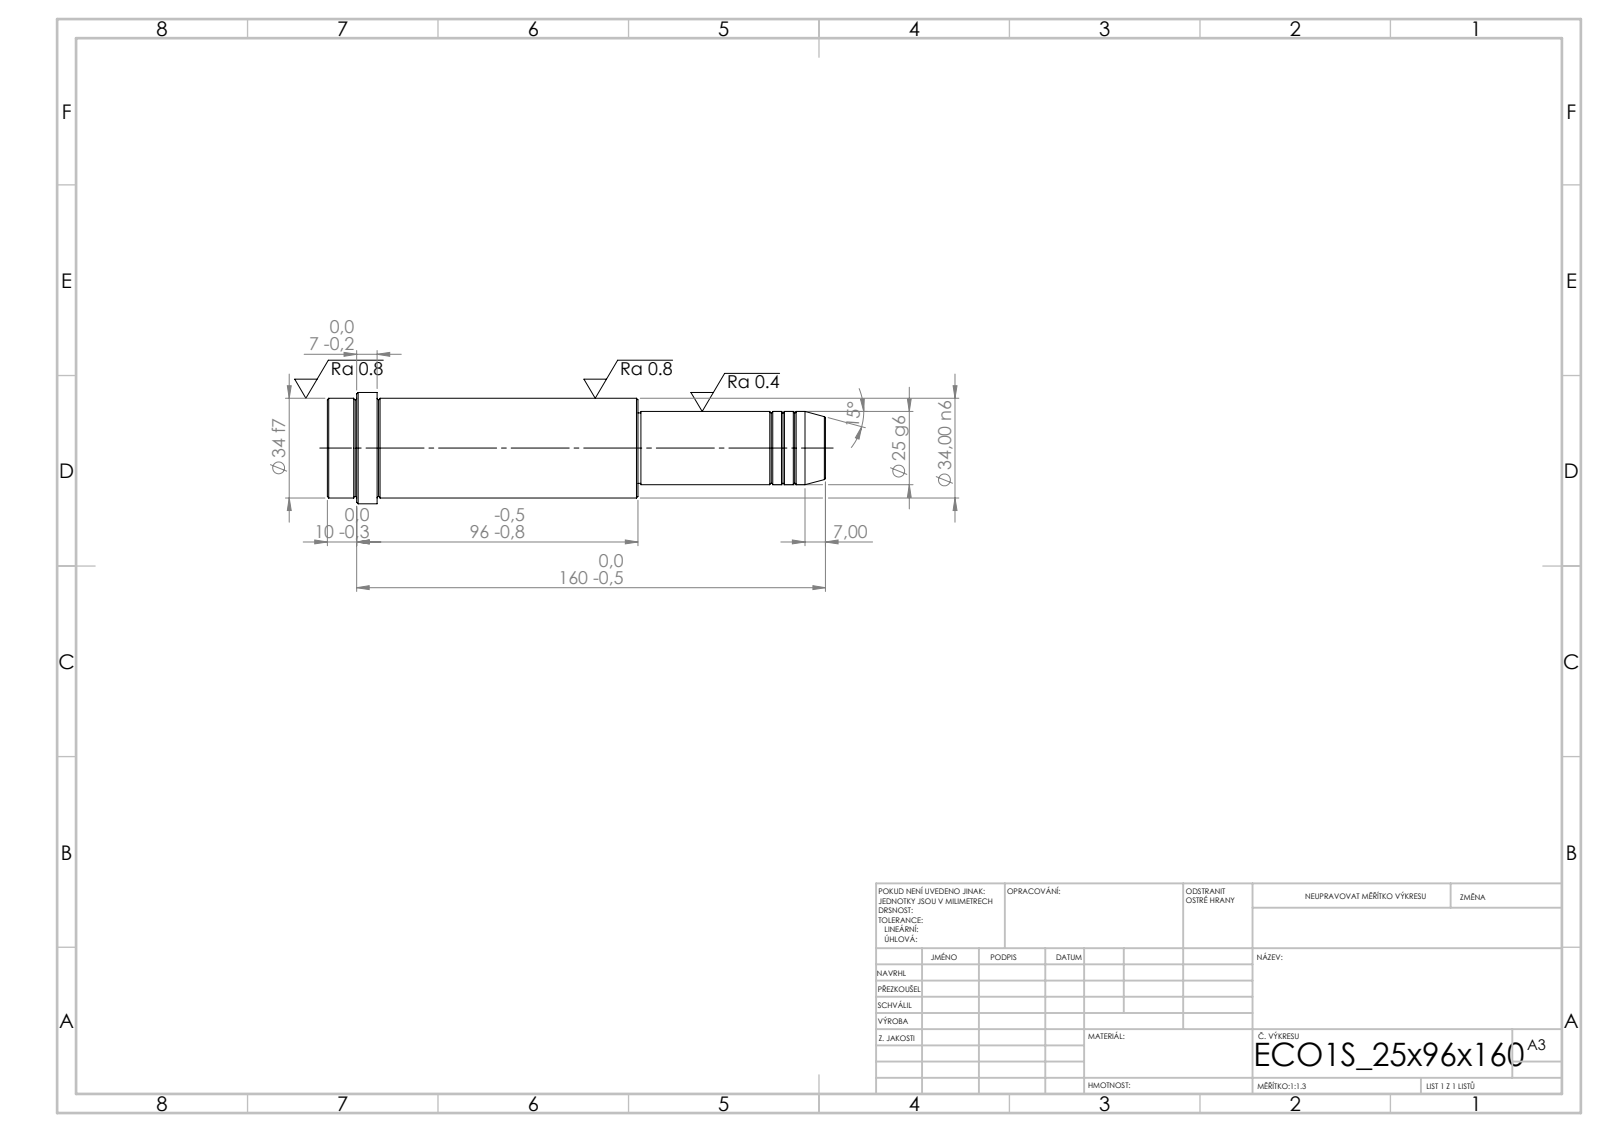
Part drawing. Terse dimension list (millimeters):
written by: SolidWorks 2019 (CONFIG_CONTROL_DESIGN)
unit: mm
bodies: 1 solid, 52 faces (6 planar, 16 cylindrical, 30 other)
size: 170 × 38 × 38
volume: 128 494 mm³; area: 18 754 mm²
bosses: 1× ⌀38, 1× ⌀34, 1× ⌀25, 1× ⌀24
face distances: 106, 64, 170, 153, 89, 17, 160, 96, 7, 10
